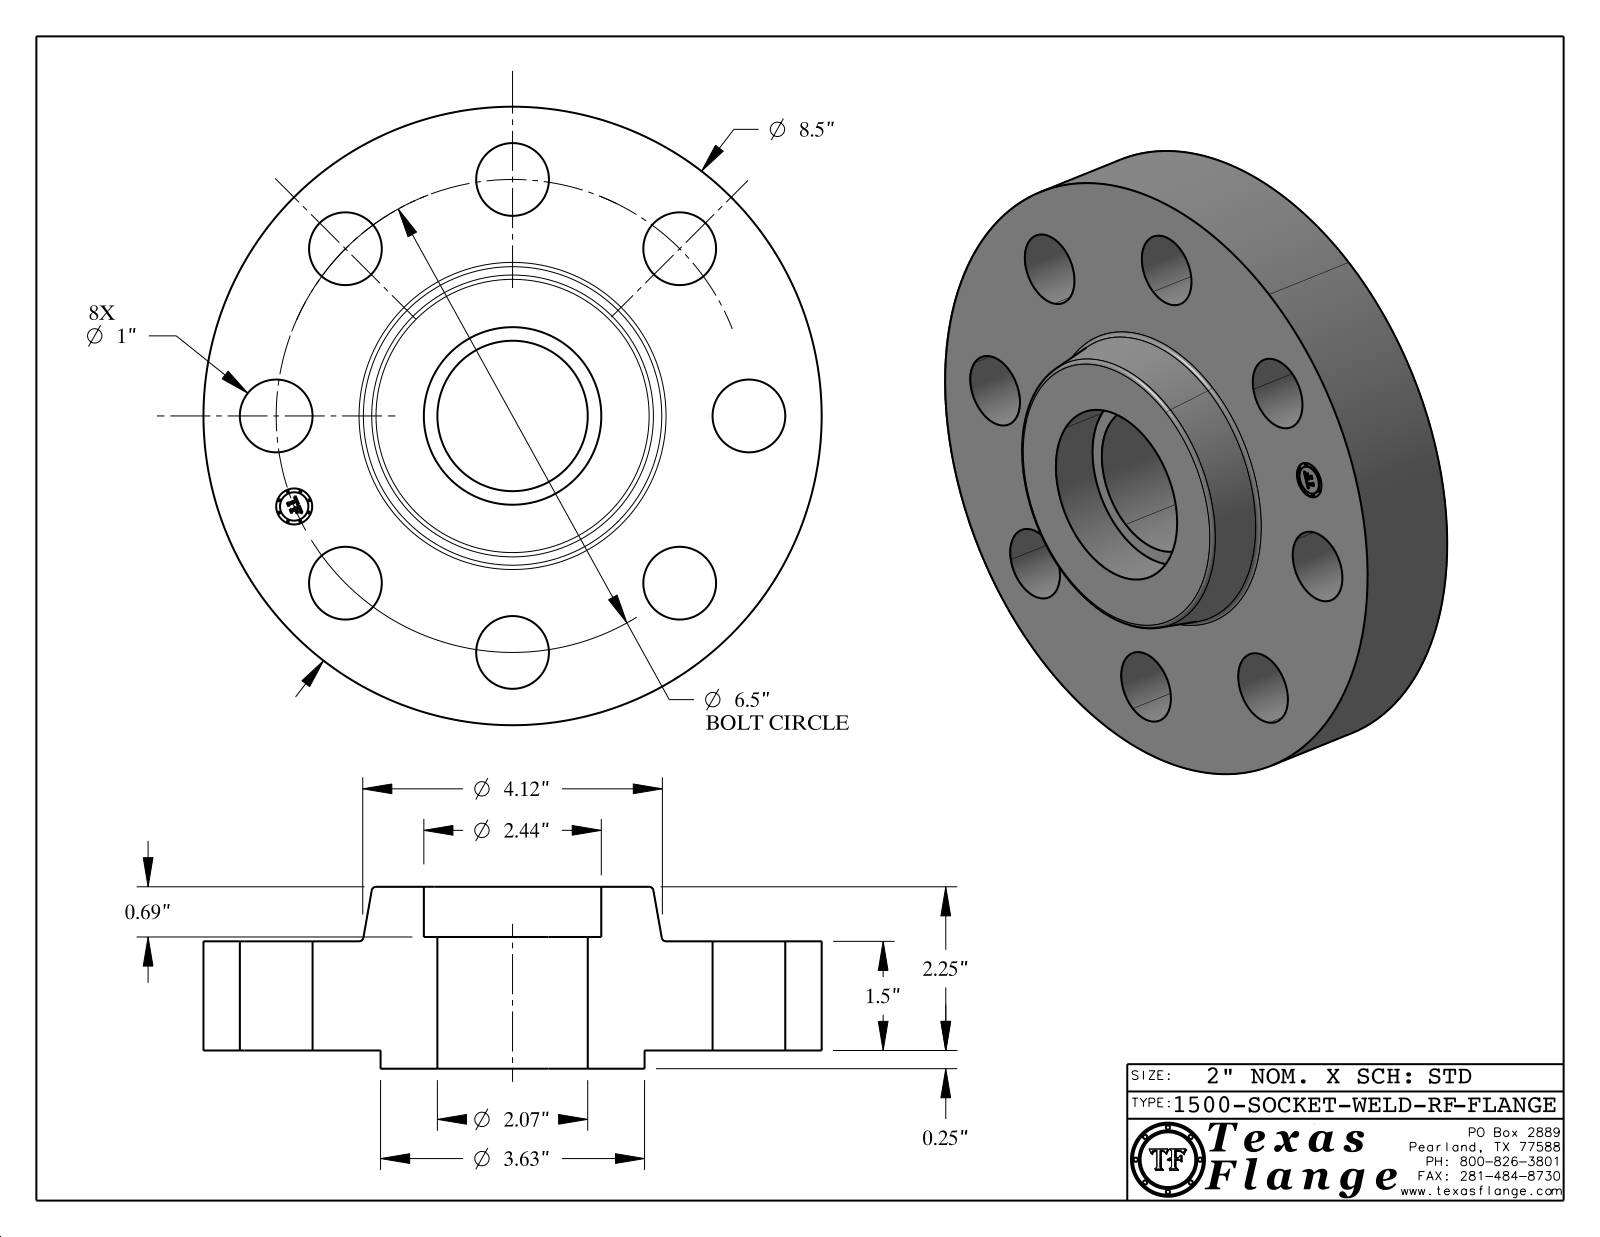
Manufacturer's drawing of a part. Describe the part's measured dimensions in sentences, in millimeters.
The part is named "1500-SOCKET-WELD-RF". Its 3-D file was written by "CATIA V5 STEP AP214 (AUTOMOTIVE_DESIGN)". It is 1 solid with 420 faces: 370 planar, 44 cylindrical and 6 other. Overall it measures 215.9 by 215.9 by 63.5 millimeters. Its volume is 1 284 000 cubic millimeters and its surface area 128 600 square millimeters. Round holes: 8 of diameter 25.4, 1 of diameter 12.6, 1 of diameter 52.5, 1 of diameter 62. Round bosses or shafts: 8 of diameter 0.8, 1 of diameter 215.9, 1 of diameter 92.2, 1 of diameter 9.9. The main face-to-face distances are 38.1, 6.4, 44.5, 63.5, 57.2, 19.1, 1.5, 46, 39.6, 17.5. The hole center spacings are 82.6, 63.2, 116.7, 152.5, 165.1, 32.2, 137.3, 161.9.
